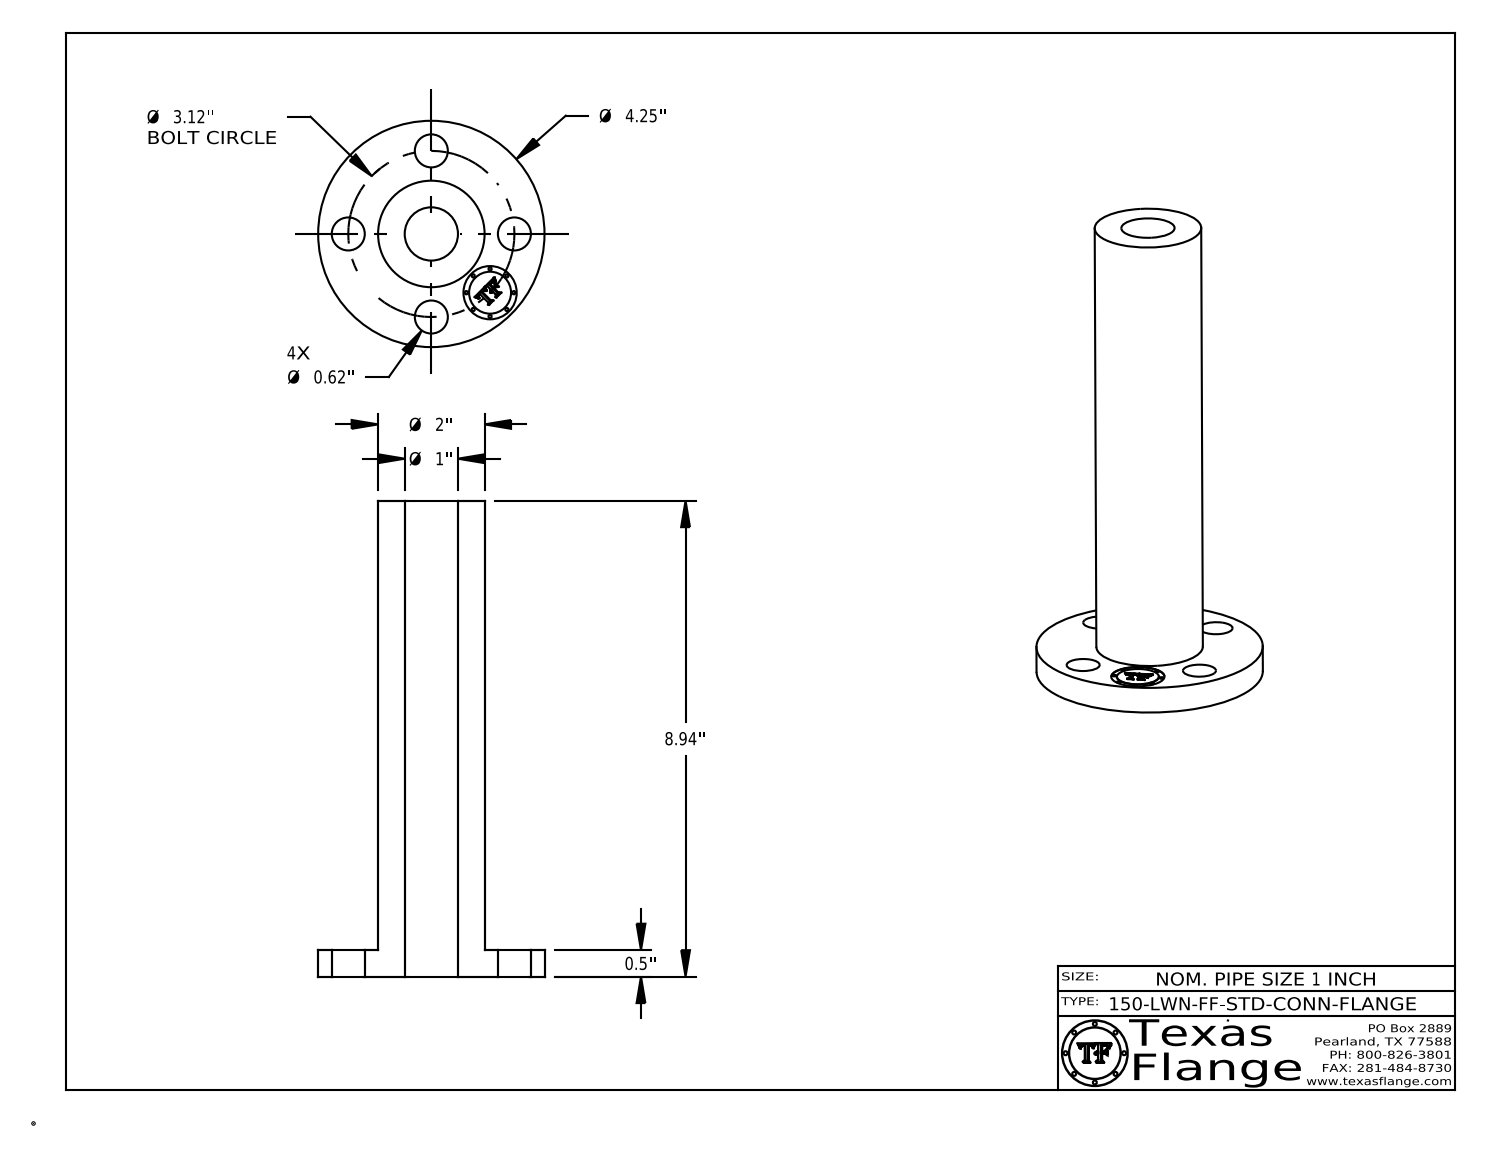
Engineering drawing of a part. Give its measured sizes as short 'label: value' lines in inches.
name: 1-150-LWN-FF-STD-CONN-FLANGE
written by: CATIA V5 STEP AP214 (AUTOMOTIVE_DESIGN)
unit: in
bodies: 1 solid, 402 faces (368 planar, 34 cylindrical, 0 other)
size: 8.938 × 4.25 × 4.25
volume: 25.95 in³; area: 116.1 in²
holes: 4× ⌀0.62, 2× ⌀1
bosses: 8× ⌀0.061, 1× ⌀4.25, 1× ⌀2, 1× ⌀0.788
face distances: 0.498, 8.937, 8.44, 0.493, 8.445, 0.298, 0.292, 0.054, 0.193, 0.248
hole spacings: 1.56, 2.206, 1.194, 2.882, 3.12, 1.56
